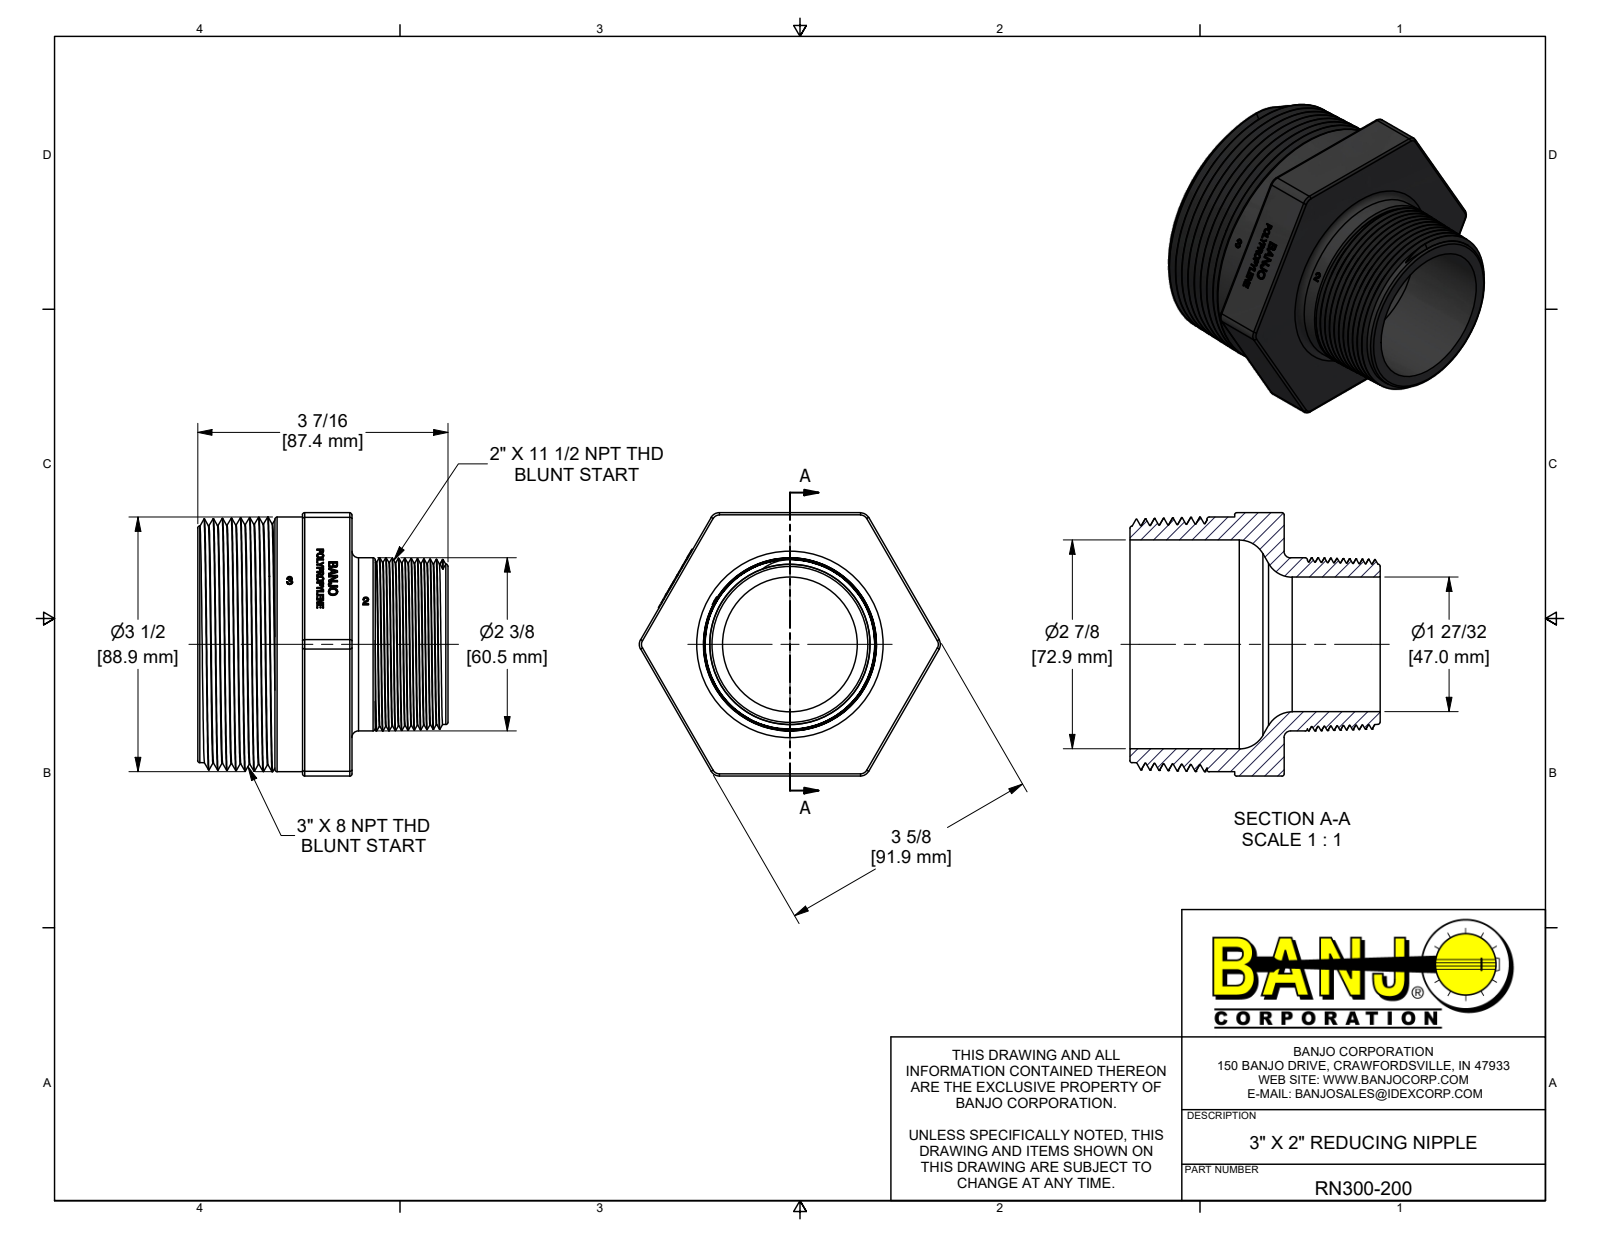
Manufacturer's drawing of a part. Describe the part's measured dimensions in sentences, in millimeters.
The part is named "RN300-200; RN300-200U". Its 3-D file was written by "Autodesk Inventor 2022 (AUTOMOTIVE_DESIGN)". It is 1 solid with 378 faces: 185 planar, 29 cylindrical and 164 other. Overall it measures 105.2 by 91.9 by 87.4 millimeters. Its volume is 165 700 cubic millimeters and its surface area 56 250 square millimeters. Round holes: 1 of diameter 47, 1 of diameter 72.9. Round bosses or shafts: 1 of diameter 88.9, 1 of diameter 60.5. Partial cylindrical surfaces (rounded edges, fillets, slot ends): 12 of radius 0.8, 6 of radius 3.3, 1 of radius 15.6, 1 of radius 23.1, 1 of radius 30.5, 1 of radius 44.7. The main face-to-face distances are 91.9, 53.8, 36.6, 17.3, 87.4, 50.8, 33.5, 9.7, 26.9, 26.9.
